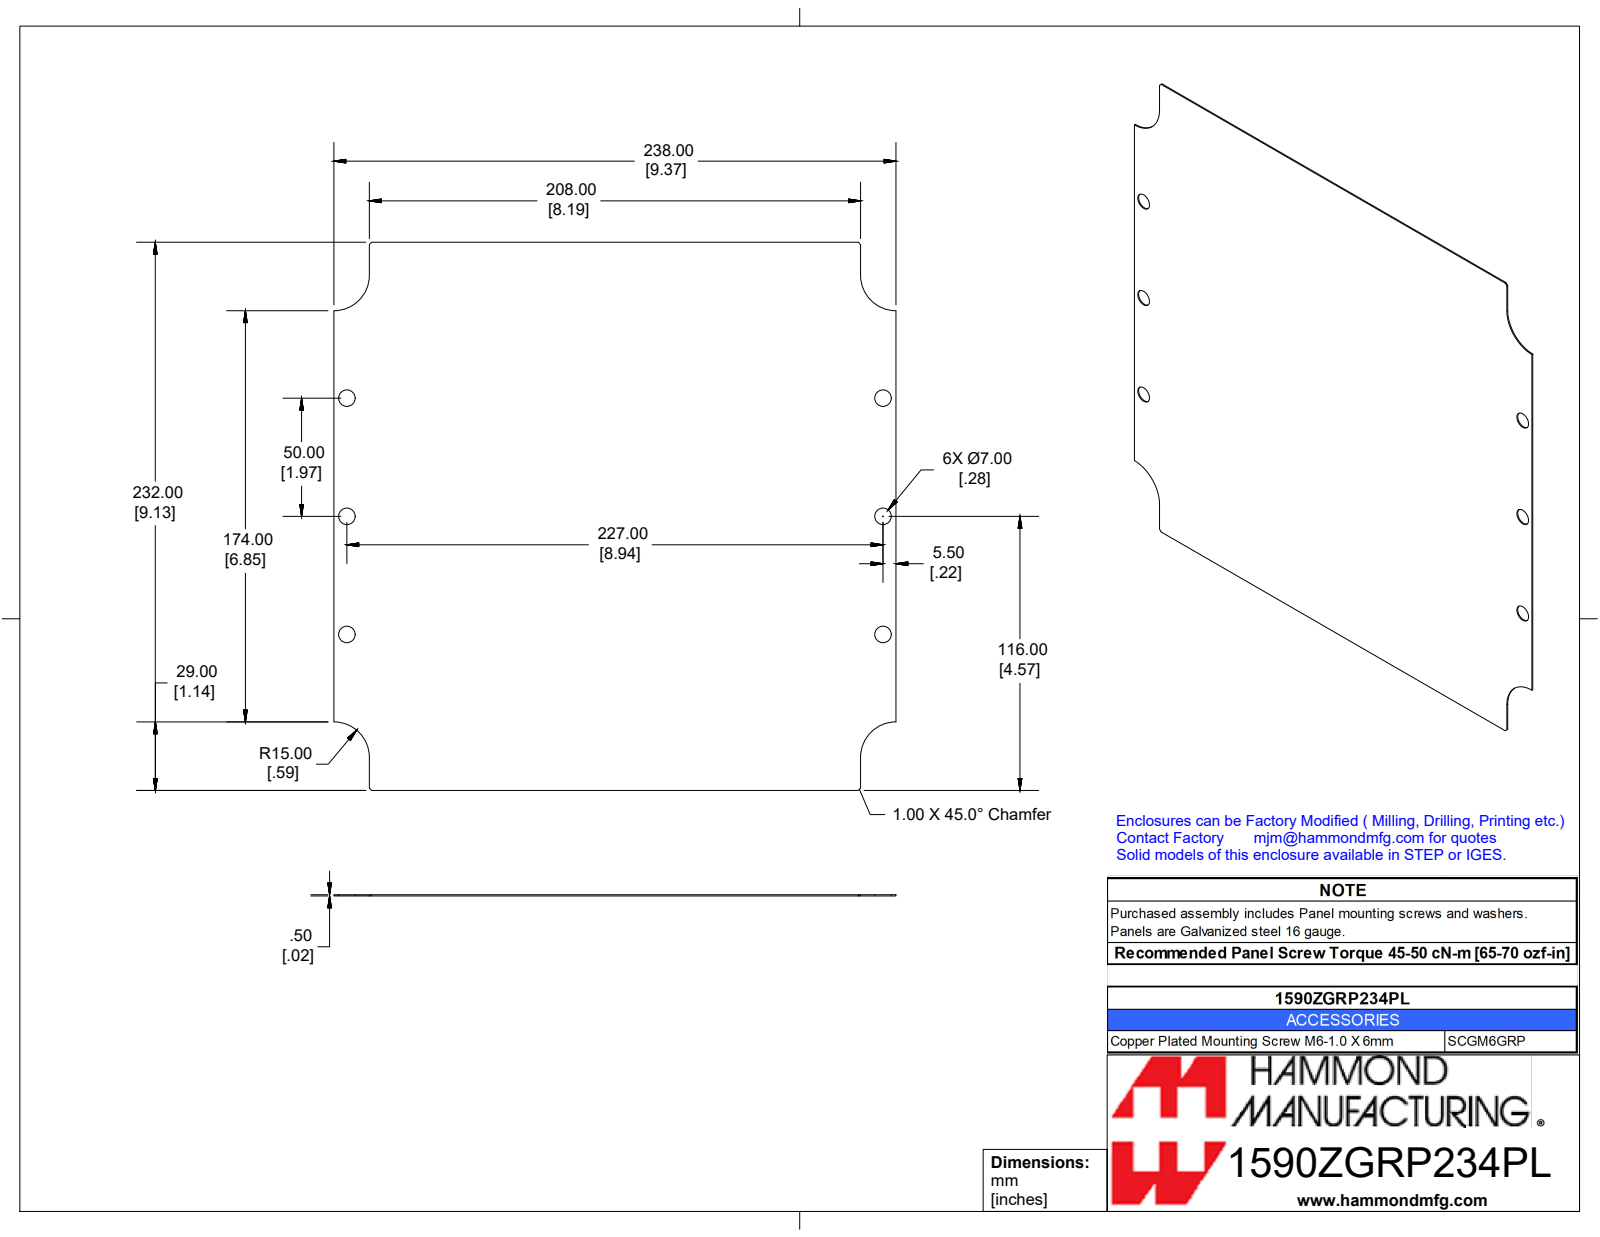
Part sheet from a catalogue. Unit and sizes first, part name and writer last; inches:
Units: inches
Overall size (bounding box): 9.37 × 9.134 × 0.02
Round holes (diameter × count): ⌀0.276 ×6
Partial cylindrical surfaces — rounded edges, fillets, slot ends (radius × count): R0.591 ×4
Main face-to-face distances: 0.02, 9.134, 9.37, 0.591, 8.78, 8.189, 12.191
Hole centre spacings: 1.969, 9.151, 8.937, 3.937, 9.766
Volume: 1.63 in³ · Surface area: 166.5 in²
Bodies: 1 solid, 24 faces (14 planar, 10 cylindrical, 0 other)
Part name (STEP PRODUCT): 1590ZGRP234PL
STEP written by: SolidWorks 2019 (CONFIG_CONTROL_DESIGN)
